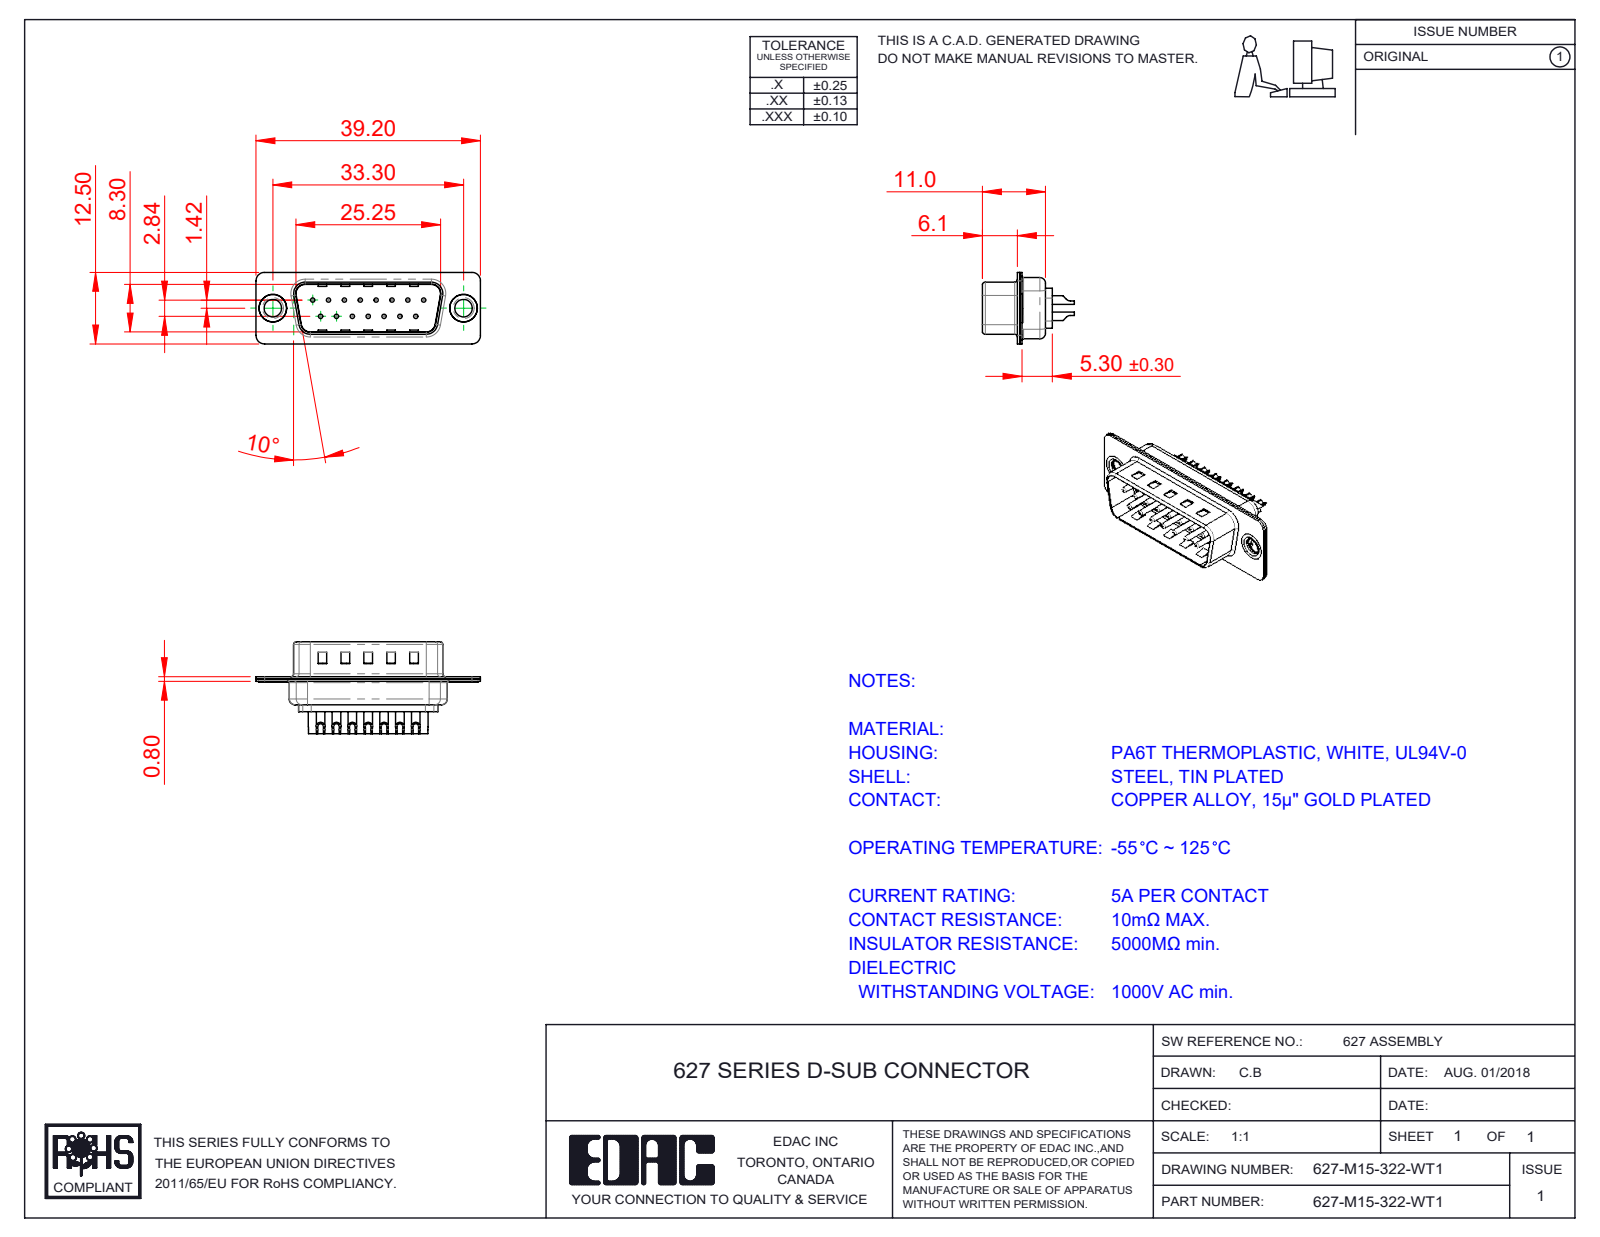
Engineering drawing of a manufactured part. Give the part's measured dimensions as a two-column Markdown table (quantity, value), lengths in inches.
| quantity | value |
| --- | --- |
| part name | 627M Contact Row 2_22; 627-M15-322-WT1; 627M Shell Front_15 Contacts; 627M Contact Row 1_22 (+3 more) |
| STEP written by | SolidWorks 2020 (CONFIG_CONTROL_DESIGN) |
| units | inches |
| bodies | 20 solids, 869 faces (274 planar, 357 cylindrical, 238 other) |
| overall size | 1.543 × 0.632 × 0.492 |
| volume | 0.11 in³ |
| surface area | 7.446 in² |
| round holes (diameter × count) | 0.03 × 15, 0.039 × 15, 0.063 × 15, 0.079 × 15, 0.12 × 2, 0.157 × 2, 0.189 × 2 |
| round bosses / shafts (diameter × count) | 0.059 × 15, 0.197 × 2, 0.193 × 2, 0.14 × 2 |
| partial cylindrical surfaces (radius × count) | 0.059 × 16, 0.079 × 12, 0.02 × 8, 0.063 × 8, 0.039 × 6, 0.01 × 4, 0.024 × 4, 0.026 × 4 |
| main face-to-face distances | 0.016, 0.031, 0.374, 0.358, 0.343, 0.39, 0.047, 0.03, 0.014, 0.24 |
| hole center spacings | 0.124, 0.109, 0.218, 0.327, 0.436, 0.198, 0.198, 0.294 |
